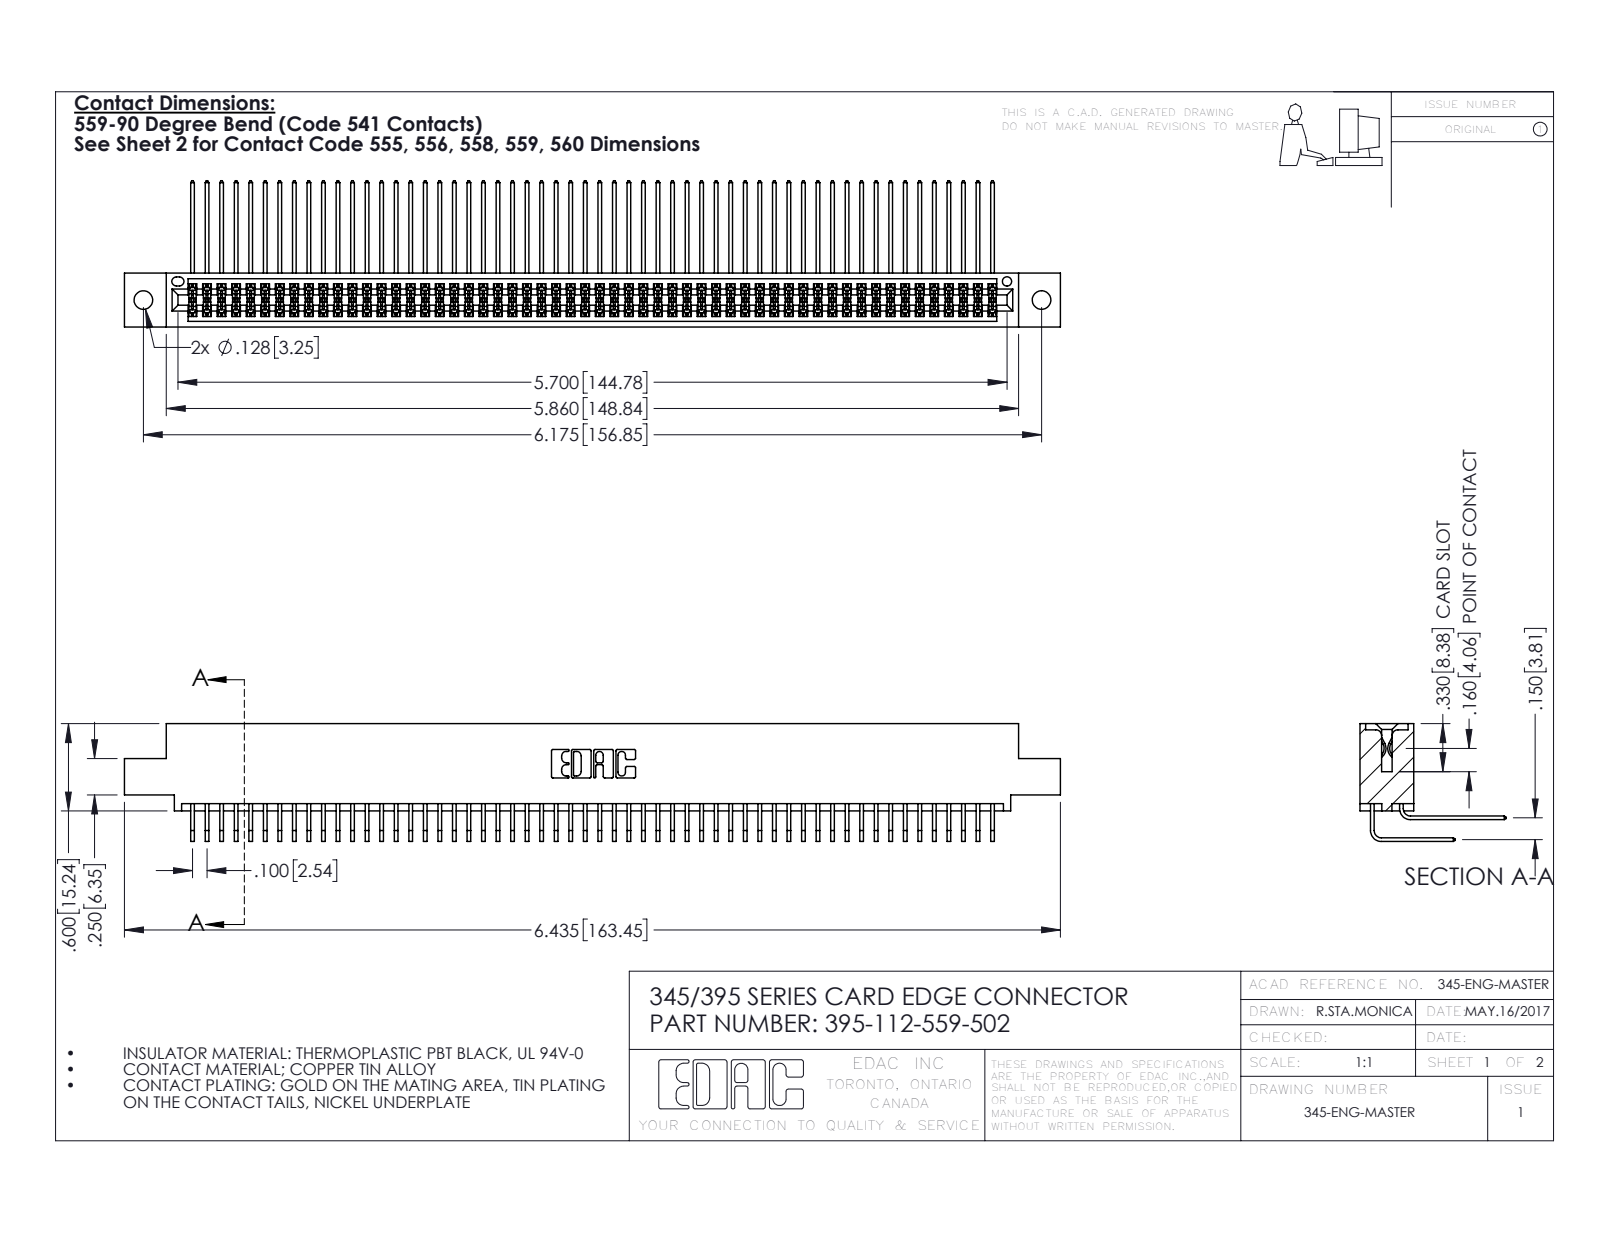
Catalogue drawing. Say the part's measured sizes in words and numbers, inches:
The part is named "345 Part_0.110 Offset - 0.128 Dia; 345-292-001_559 Tail - 2; 345-292-001_558 559 Tail - 1; 395-112-559-502". Its 3-D file was written by "SolidWorks 2016 (CONFIG_CONTROL_DESIGN)". It is 113 solids with 5954 faces: 4004 planar, 1950 cylindrical and 0 other. Overall it measures 6.435 by 1.005 by 0.809 inches. Its volume is 1.01 cubic inches and its surface area 42.75 square inches. Round holes: 2 of diameter 0.128, 1 of diameter 0.064. Partial cylindrical surfaces (rounded edges, fillets, slot ends): 169 of radius 0.006, 22 of radius 0.01, 6 of radius 0.007, 6 of radius 0.031, 3 of radius 0.026, 2 of radius 0.014, 2 of radius 0.019, 2 of radius 0.022. The main face-to-face distances are 0.072, 0.298, 0.2, 0.37, 0.098, 0.272, 0.025, 0.225, 0.175, 0.15. The hole center spacings are 0.27, 5.939, 6.175.
